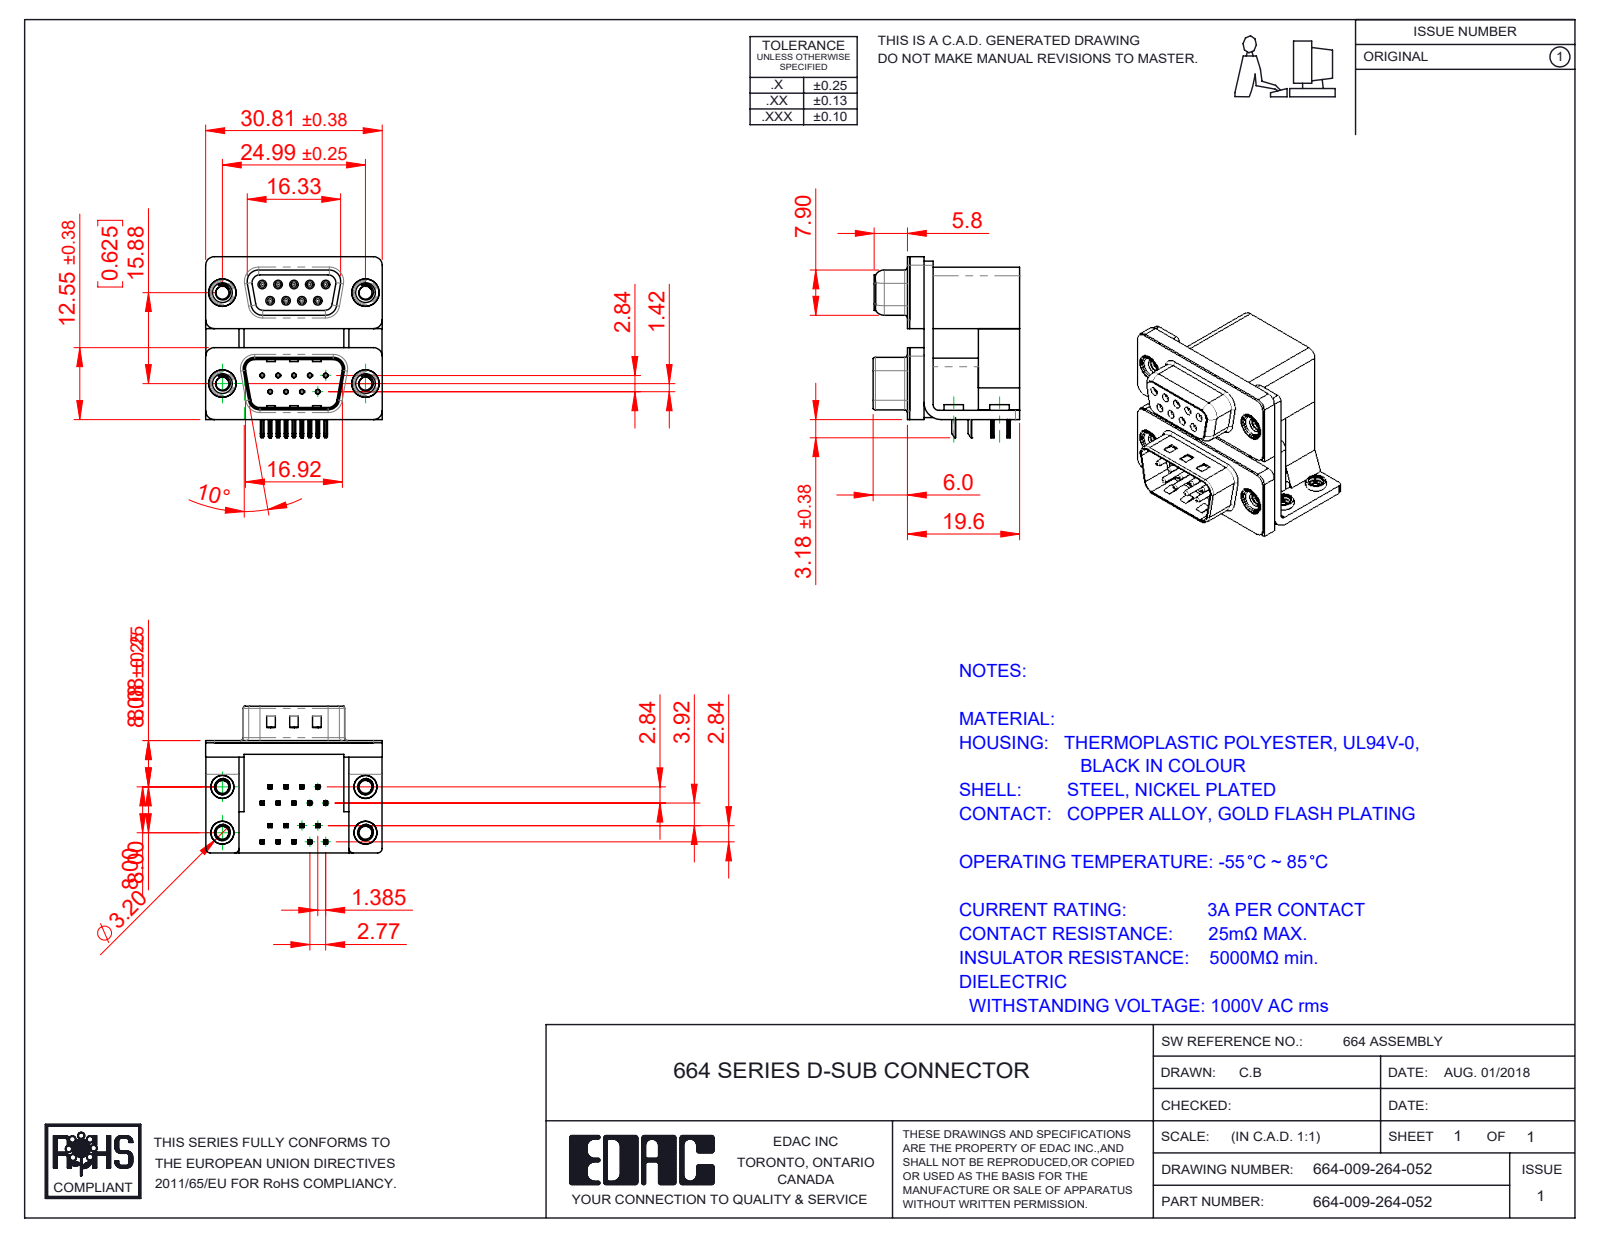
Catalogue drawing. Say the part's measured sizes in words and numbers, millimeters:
The part is named "664 Shell Receptacle_09 Contacts; 664 Contact Top Lower; 664 Housing Spacer_09 Contacts L; 664 Contact Bottom Lower (+8 more)". Its 3-D file was written by "SolidWorks 2020 (CONFIG_CONTROL_DESIGN)". It is 33 solids with 2669 faces: 1275 planar, 771 cylindrical and 623 other. Overall it measures 31.61 by 30.81 by 25.6 millimeters. Its volume is 10 359 cubic millimeters and its surface area 12 382 square millimeters. Round holes: 18 of diameter 0.8, 9 of diameter 0.35, 9 of diameter 0.9, 8 of diameter 2.26, 4 of diameter 2.75, 4 of diameter 3.2, 4 of diameter 3.5, 4 of diameter 4, 4 of diameter 4.8, 4 of diameter 5. Round bosses or shafts: 9 of diameter 1.2, 9 of diameter 0.75, 4 of diameter 4.9, 4 of diameter 4.75, 4 of diameter 4, 4 of diameter 3.9, 4 of diameter 3.4. Partial cylindrical surfaces (rounded edges, fillets, slot ends): 72 of radius 0.1, 36 of radius 0.15, 36 of radius 0.25, 18 of radius 0.12, 18 of radius 0.35, 13 of radius 1.5, 12 of radius 0.5, 10 of radius 1.35. The main face-to-face distances are 0.4, 2.5, 16.7, 19.2, 19.6, 2.9, 7.2, 9.5, 12, 12.4. The hole center spacings are 3.16, 2.77, 16.12, 15.88, 5.54, 16.82, 13.11, 18.77.
